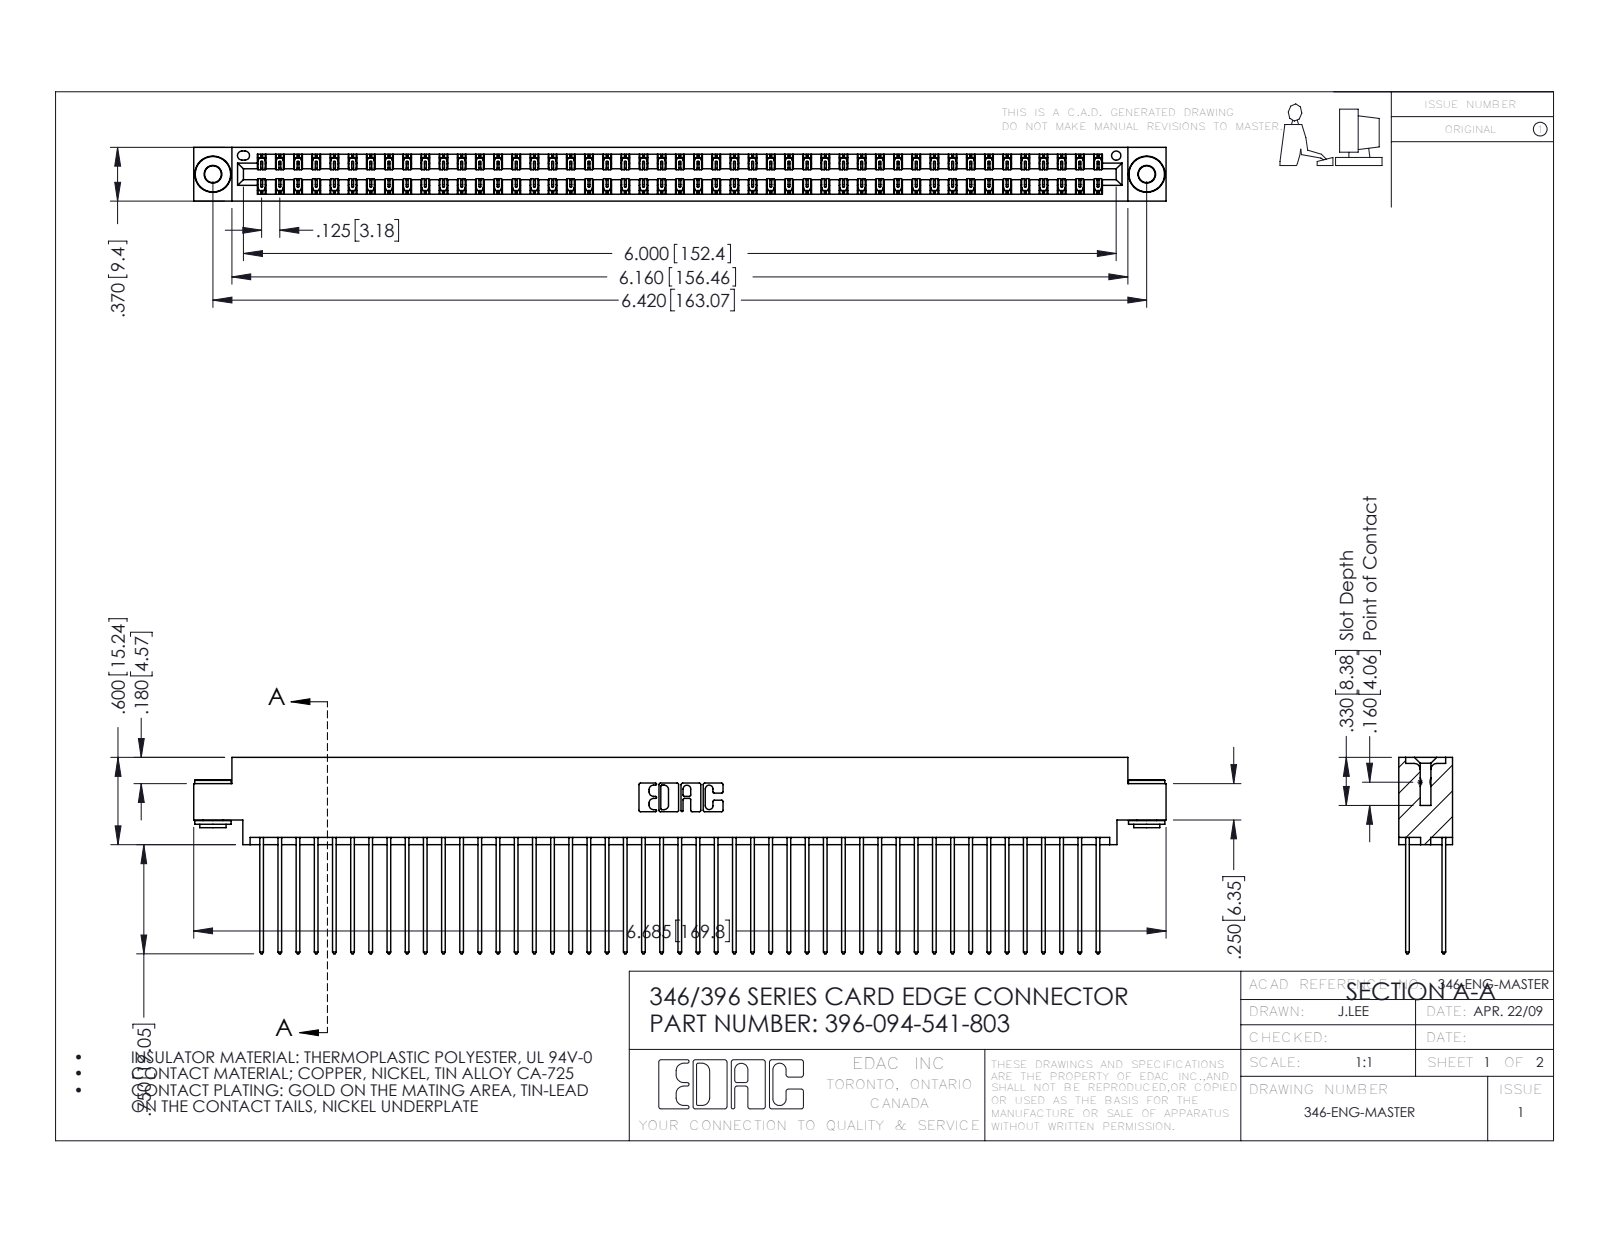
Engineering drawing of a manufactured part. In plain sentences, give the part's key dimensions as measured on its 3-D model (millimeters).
The part is named "396-094-541-803; 345-292-001_345-293-141; 345-250-002_345-250-002-102; 346 Part_0.170 Offset - 0.156 Dia-TH". Its 3-D file was written by "SolidWorks 2016 (CONFIG_CONTROL_DESIGN)". It is 97 solids with 5052 faces: 3380 planar, 1664 cylindrical and 8 other. Overall it measures 169.8 by 34.3 by 9.4 millimeters. Its volume is 16 990 cubic millimeters and its surface area 26 430 square millimeters. Round holes: 2 of diameter 2.9, 2 of diameter 4, 1 of diameter 1.6. Round bosses or shafts: 2 of diameter 6.4, 2 of diameter 4.6, 2 of diameter 3.5. Partial cylindrical surfaces (rounded edges, fillets, slot ends): 141 of radius 0.2, 94 of radius 0.3, 22 of radius 0.3, 6 of radius 0.2, 6 of radius 0.8, 3 of radius 0.7, 2 of radius 0.4, 2 of radius 0.6. The main face-to-face distances are 1.2, 8.2, 6.4, 0.6, 1.8, 7.6, 9.4, 7, 5.7, 3.8. The hole center spacings are 6.2, 157.8, 163.1.
